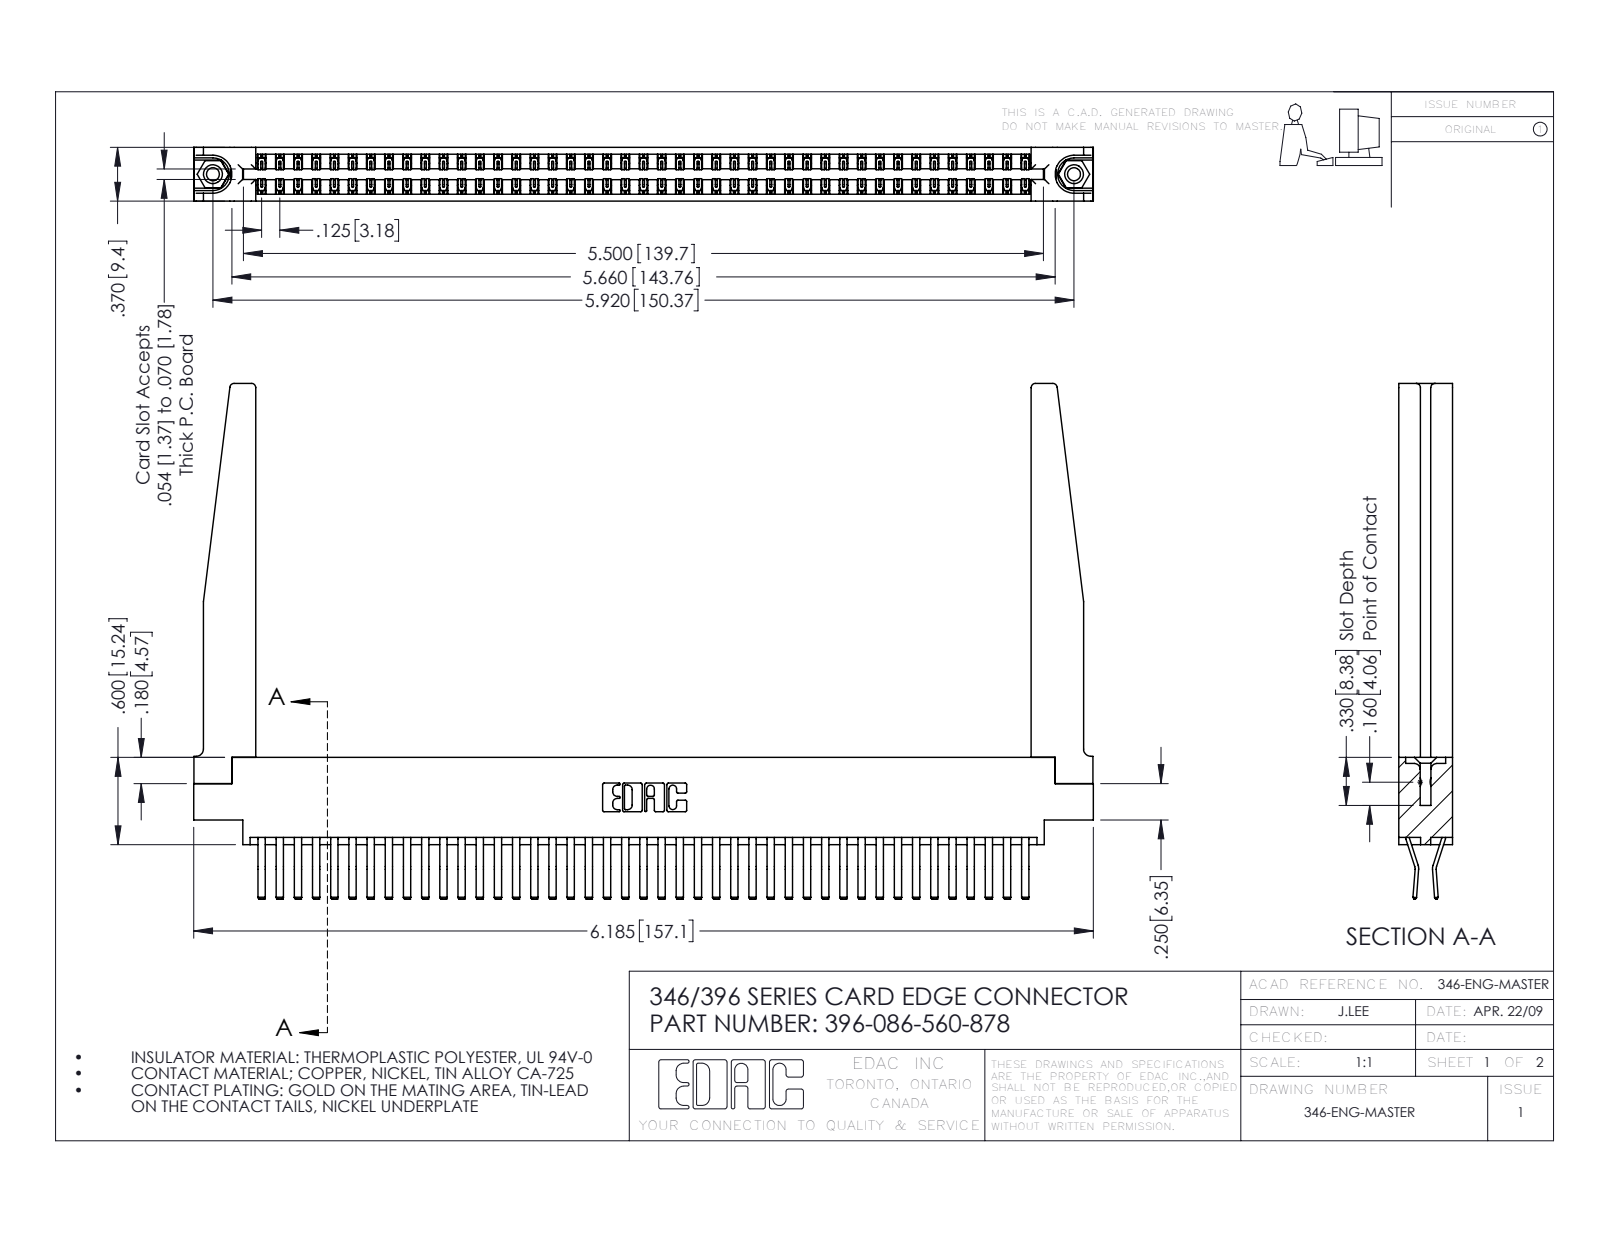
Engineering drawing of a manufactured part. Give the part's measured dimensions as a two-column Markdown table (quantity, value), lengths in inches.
| quantity | value |
| --- | --- |
| part name | 345-292-001_560 Tail; 346 Part_0.170 Offset - 0.156 Dia-TH; 345-250-001_345-250-001-102; 346-220-078_345-220-078 (+1 more) |
| STEP written by | SolidWorks 2016 (CONFIG_CONTROL_DESIGN) |
| units | inches |
| bodies | 91 solids, 5004 faces (3232 planar, 1720 cylindrical, 52 other) |
| overall size | 6.185 × 3.545 × 0.37 |
| volume | 1.382 in³ |
| surface area | 46.29 in² |
| round holes (diameter × count) | 0.089 × 2, 0.125 × 2, 0.156 × 2, 0.064 × 1 |
| round bosses / shafts (diameter × count) | 0.155 × 2 |
| partial cylindrical surfaces (radius × count) | 0.006 × 129, 0.01 × 22, 0.03 × 8, 0.007 × 6, 0.031 × 6, 0.05 × 4, 0.026 × 3, 0.01 × 2 |
| main face-to-face distances | 0.37, 0.048, 0.322, 0.072, 0.025, 0.148, 0.15, 0.25, 0.298, 0.275 |
| hole center spacings | 0.246, 5.711, 5.92 |
